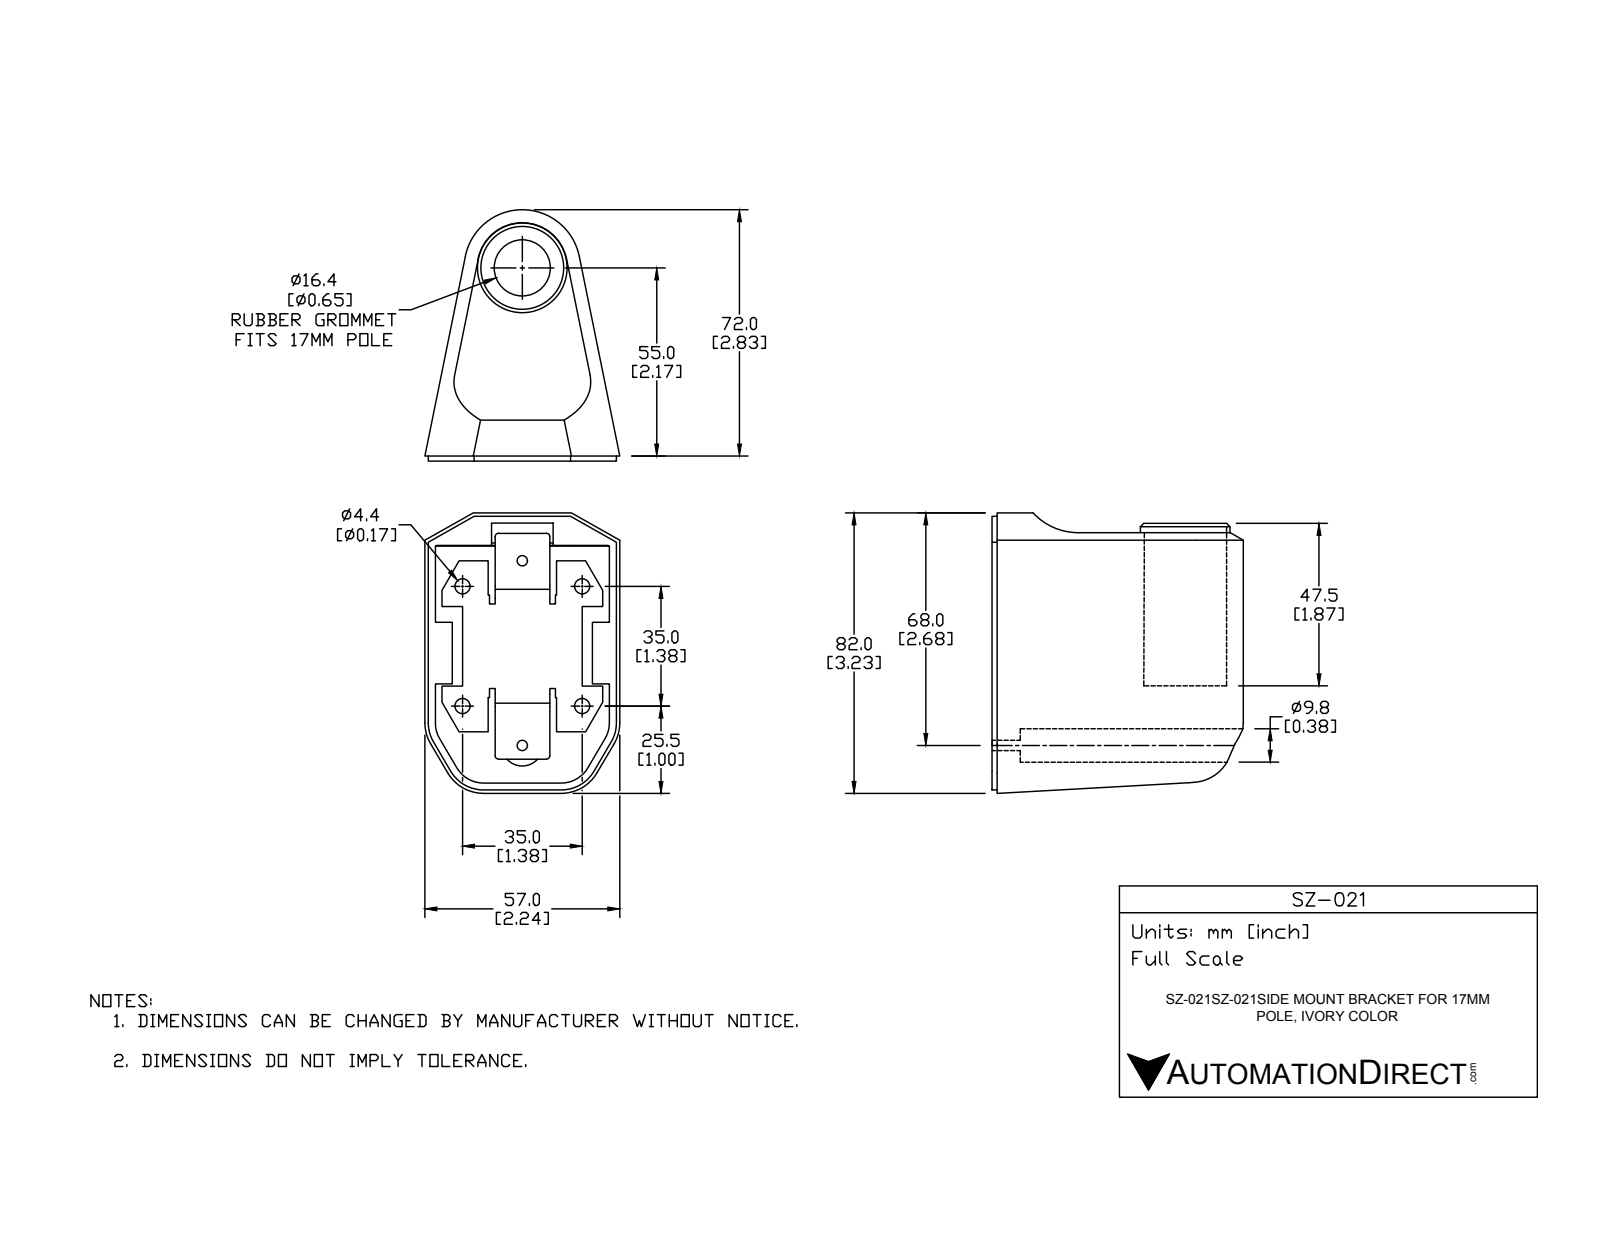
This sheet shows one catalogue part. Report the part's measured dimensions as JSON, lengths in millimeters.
{"part_name": "SZ-021", "step_written_by": "SolidWorks 2016 (AUTOMOTIVE_DESIGN)", "units": "millimeters", "bodies": {"solids": 4, "faces": 205, "planar": 131, "cylindrical": 50, "other": 24}, "overall_size": [82, 73.5, 57], "volume_mm3": 58926, "surface_area_mm2": 44996, "round_holes": [[4.4, 4], [3, 2], [4.8, 1], [9.8, 1], [16.4, 1], [18, 1]], "round_bosses_or_shafts": [[26.2, 1], [12, 1]], "partial_cylinders_radius": [[1, 8], [2.65, 4], [9, 4], [12, 4], [14, 1], [17, 1], [18, 1], [21, 1]], "face_to_face_distances": [3, 3.01, 1.65, 3.7, 7.38, 1.5, 3.15, 0.7, 41, 8.88], "hole_center_spacings": [35, 19.04, 20.94, 45.96, 49.5, 49.68, 54]}
